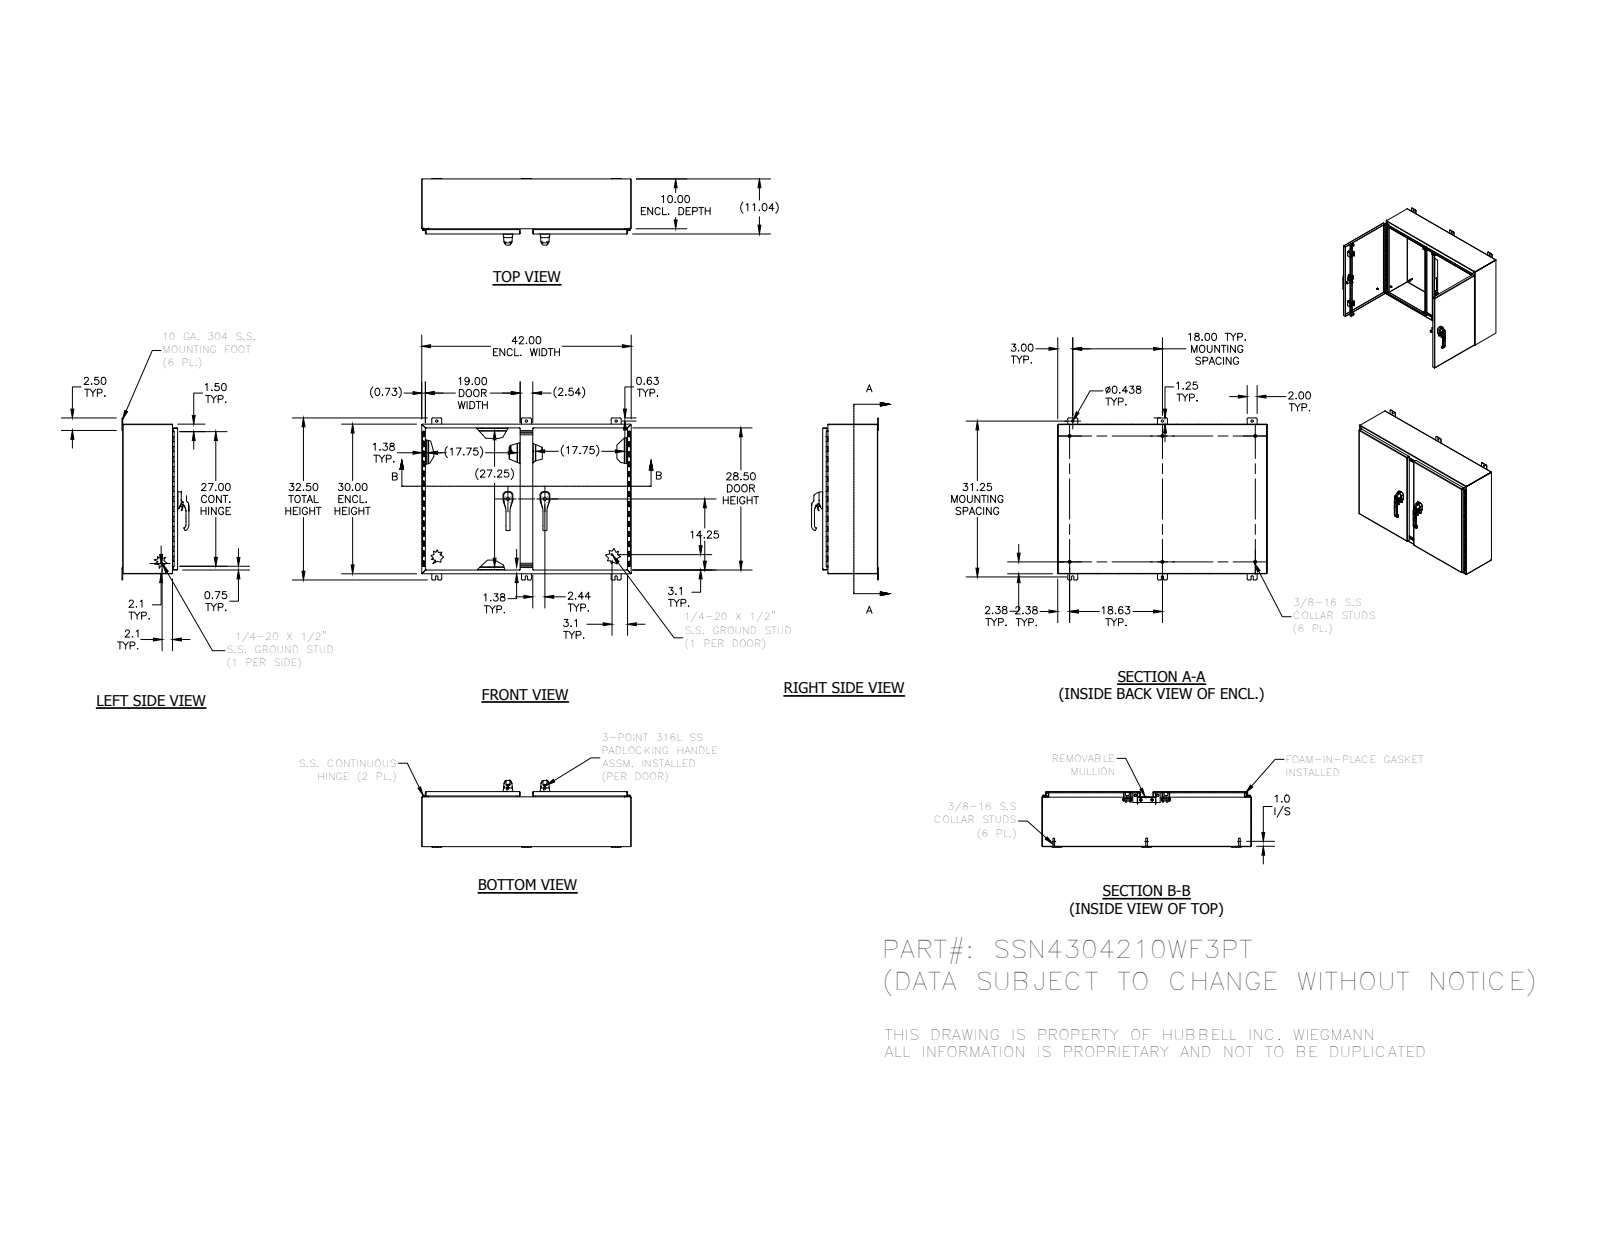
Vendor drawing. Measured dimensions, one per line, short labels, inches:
name: 38846; 328139L; PLASTIC-ROLLER-CAM_AF0_ASM; SSN43010WF3PTLRS (+8 more)
written by: SolidWorks 2014 (AUTOMOTIVE_DESIGN)
unit: in
bodies: 125 solids, 6482 faces (2308 planar, 2658 cylindrical, 1516 other)
size: 42 × 32.5 × 13.409
volume: 408.1 in³; area: 10 009 in²
holes: 12× ⌀0.262, 8× ⌀0.187, 6× ⌀0.213, 6× ⌀0.28, 6× ⌀0.438, 4× ⌀0.196, 4× ⌀0.252, 4× ⌀0.281, 4× ⌀0.315, 4× ⌀0.4, 4× ⌀0.402, 4× ⌀0.45
bosses: 9× ⌀0.25, 6× ⌀0.625, 6× ⌀0.533, 6× ⌀0.33, 5× ⌀0.236, 4× ⌀0.531, 4× ⌀0.438, 4× ⌀0.435
rounds: 317× R0.02, 221× R0.012, 39× R0.019, 33× R0.031, 31× R0.125, 30× R0.05, 30× R0.25, 25× R0.079
face distances: 0.074, 0.094, 10.942, 10.868, 11.035, 10.961, 29.926, 9.926, 41.926, 29.852
hole spacings: 0.38, 0.76, 7.417, 0.492, 0.492, 0.886, 1.236, 1.376
